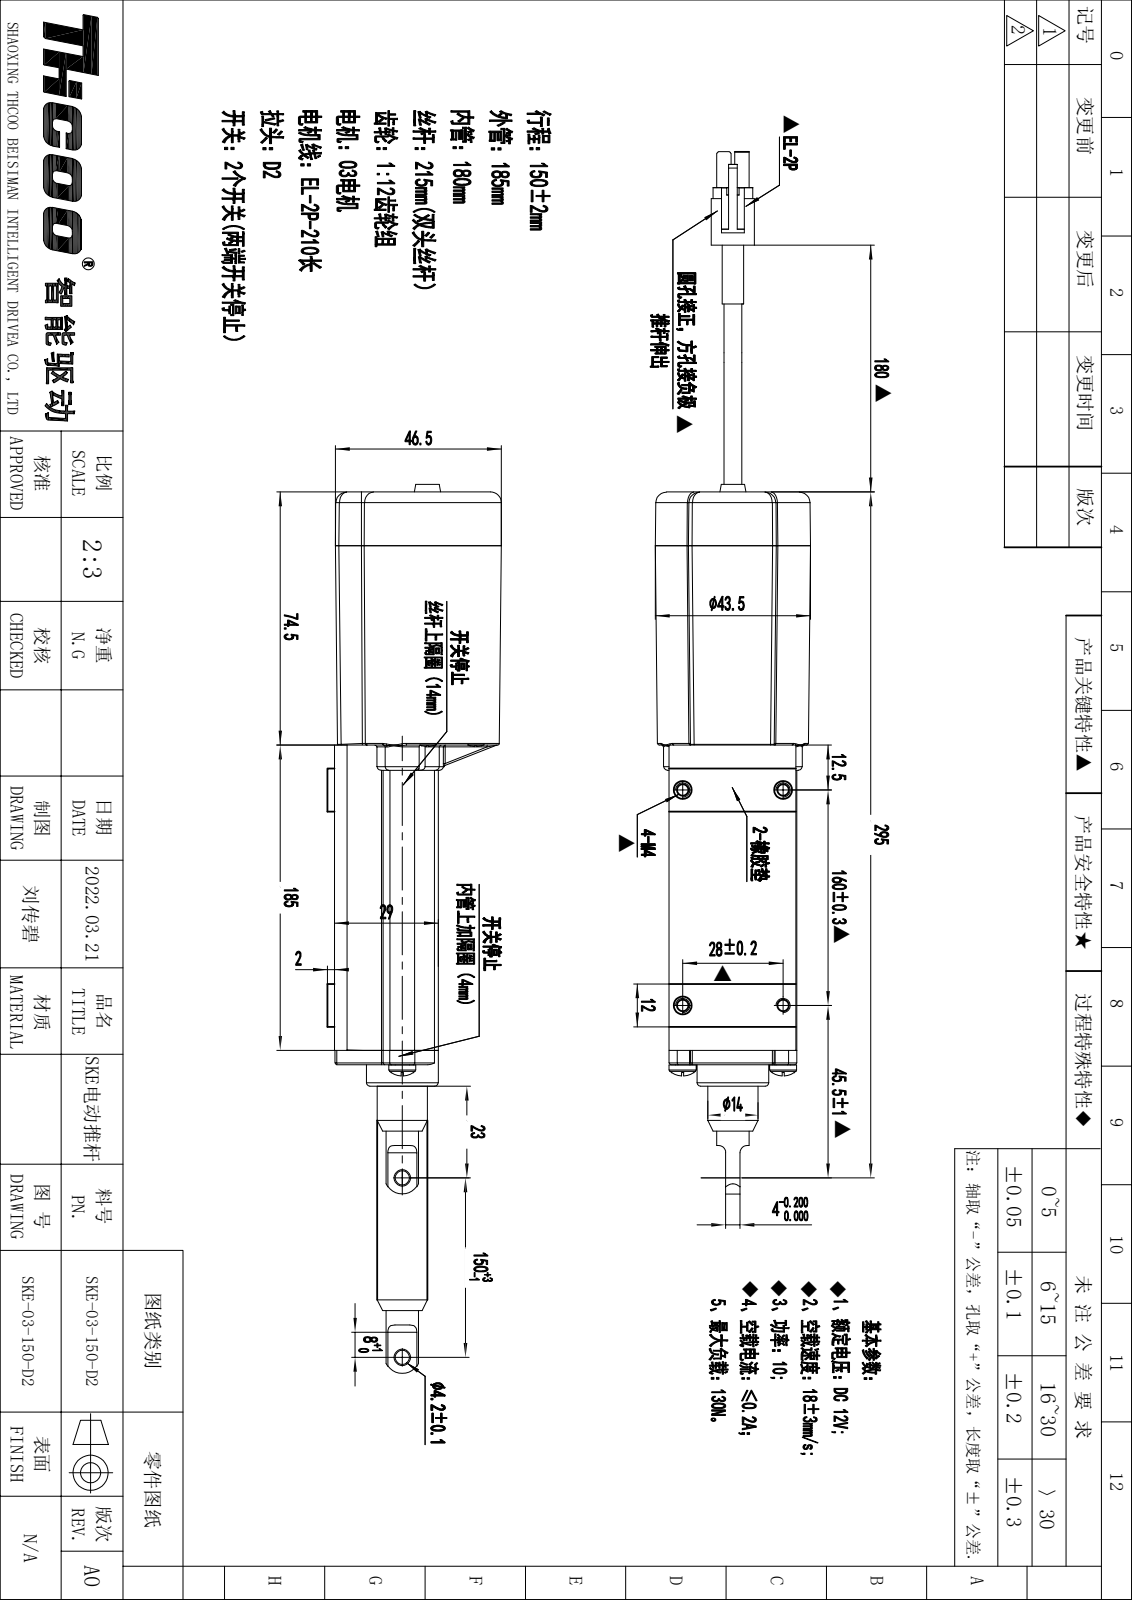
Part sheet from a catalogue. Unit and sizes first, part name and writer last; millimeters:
Units: millimetres
Overall size (bounding box): 370.13 × 48.47 × 43.25
Round holes (diameter × count): ⌀4 ×4, ⌀4.8 ×4, ⌀3.2 ×3, ⌀4.2 ×3, ⌀5 ×3, ⌀6.3 ×1, ⌀7 ×1, ⌀8.2 ×1, ⌀10 ×1, ⌀14.2 ×1, ⌀16 ×1
Round bosses / shafts (diameter × count): ⌀7.5 ×2, ⌀4 ×2, ⌀20 ×1, ⌀15.9 ×1, ⌀15 ×1, ⌀14 ×1, ⌀12 ×1, ⌀9 ×1
Partial cylindrical surfaces — rounded edges, fillets, slot ends (radius × count): R0.5 ×97, R1 ×19, R0.2 ×8, R0.4 ×7, R2 ×6, R3 ×6, R1.08 ×4, R1.8 ×4
Main face-to-face distances: 2, 21.3, 1.5, 3.5, 23.3, 6, 2.5, 4, 8, 20
Hole centre spacings: 28, 7.16, 14, 17.01, 30.32, 170, 172.29, 15.51
Volume: 136 138 mm³ · Surface area: 121 314 mm²
Bodies: 8 solids, 773 faces (321 planar, 248 cylindrical, 204 other)
Part name (STEP PRODUCT): Admi0CB42C5Fkidw
STEP written by: SIEMENS PLM Software NX 12.0 (AUTOMOTIVE_DESIGN)
